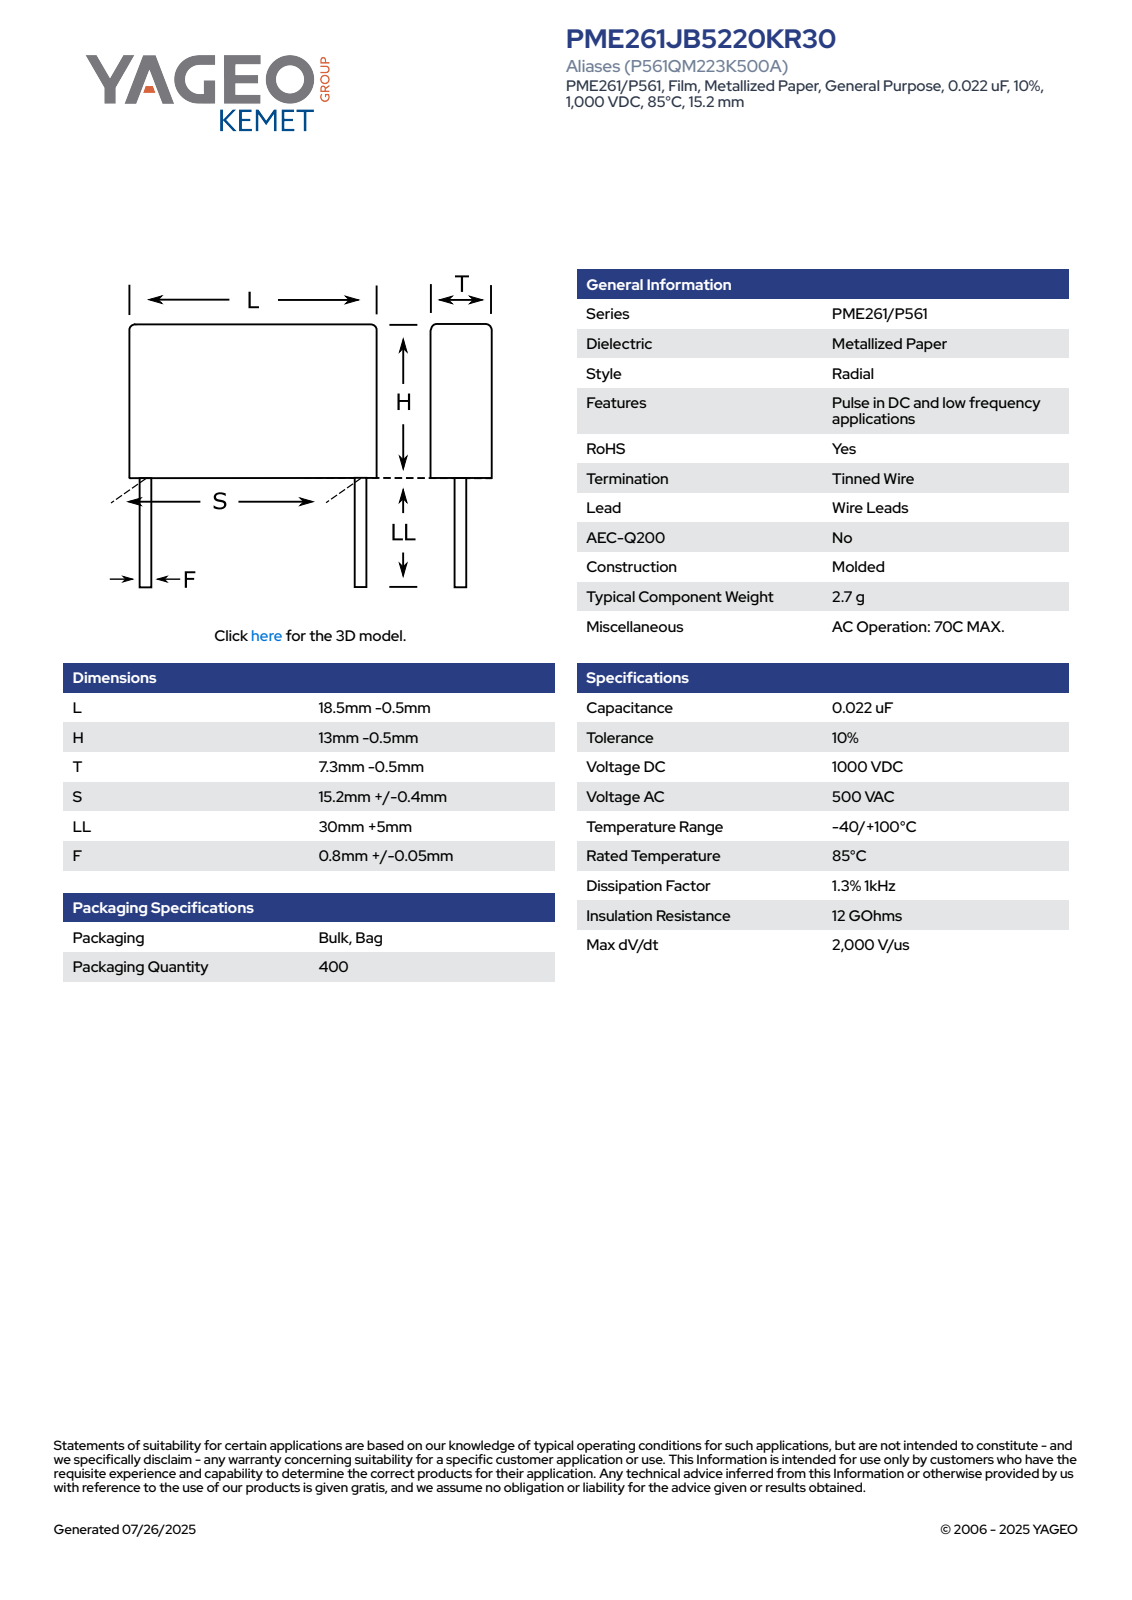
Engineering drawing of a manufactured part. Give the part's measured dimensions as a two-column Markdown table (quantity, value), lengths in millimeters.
| quantity | value |
| --- | --- |
| part name | CFR_MOLDED_18.5X13X7.3_L18H12.5T6.8S15.2LL35F0.85 |
| STEP written by | SolidWorks 2014 (AUTOMOTIVE_DESIGN) |
| units | millimeters |
| bodies | 4 solids, 73 faces (65 planar, 8 cylindrical, 0 other) |
| overall size | 47.5 × 18 × 6.8 |
| volume | 1 567 mm³ |
| surface area | 1 057 mm² |
| round bosses / shafts (diameter × count) | 0.85 × 2 |
| partial cylindrical surfaces (radius × count) | 0.5 × 4 |
| main face-to-face distances | 6.8, 12.5, 18, 35, 47.5, 41.85, 6.85, 5.65, 40.24, 5.24 |
